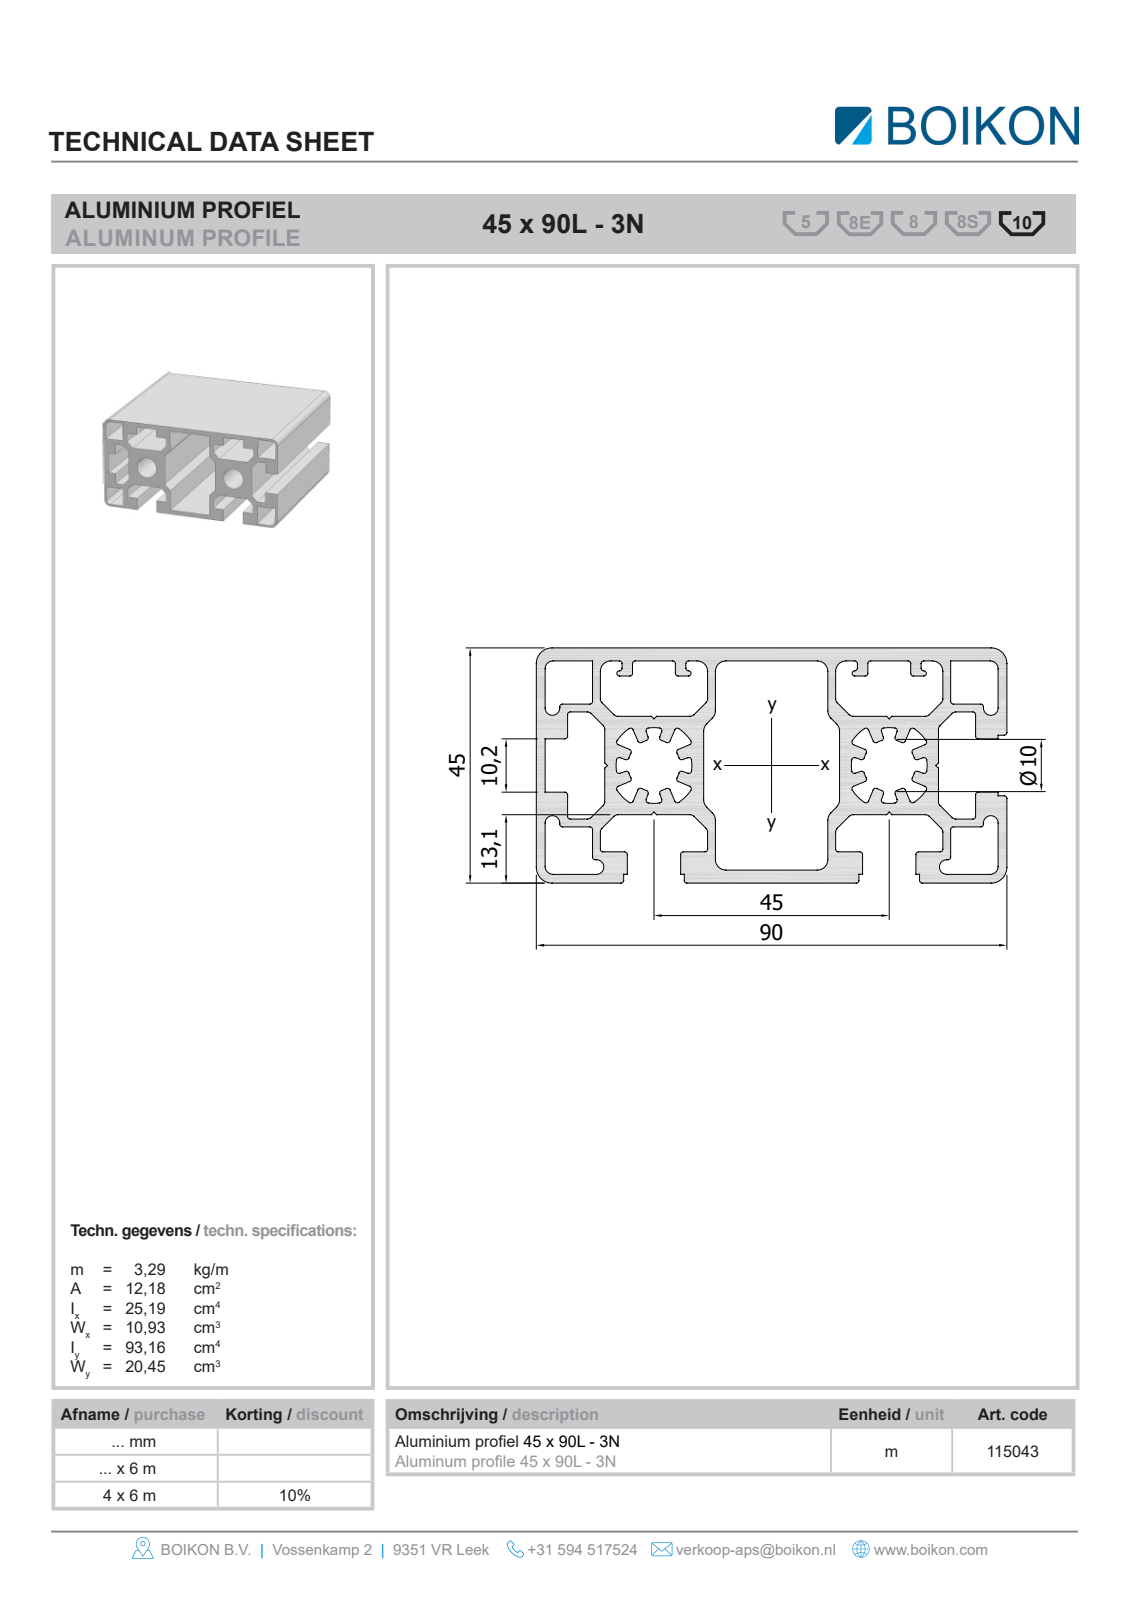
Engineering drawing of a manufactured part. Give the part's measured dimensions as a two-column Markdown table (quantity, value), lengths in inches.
| quantity | value |
| --- | --- |
| part name | Root; 11504345x90L-3NBOIKON0 |
| STEP written by | HiCAD 2013 1802.4 Build 509 (AUTOMOTIVE_DESIGN) |
| units | inches |
| bodies | 1 solid, 104 faces (94 planar, 10 cylindrical, 0 other) |
| overall size | 39.37 × 3.543 × 1.772 |
| volume | 91.96 in³ |
| surface area | 1 407 in² |
| round holes (diameter × count) | 0.402 × 2 |
| partial cylindrical surfaces (radius × count) | 0.079 × 4, 0.118 × 4 |
| main face-to-face distances | 1.772, 0.516, 1.256, 0.394, 1.688, 0.122, 0.862, 0.236, 0.28, 1.02 |
| hole center spacings | 1.772 |
